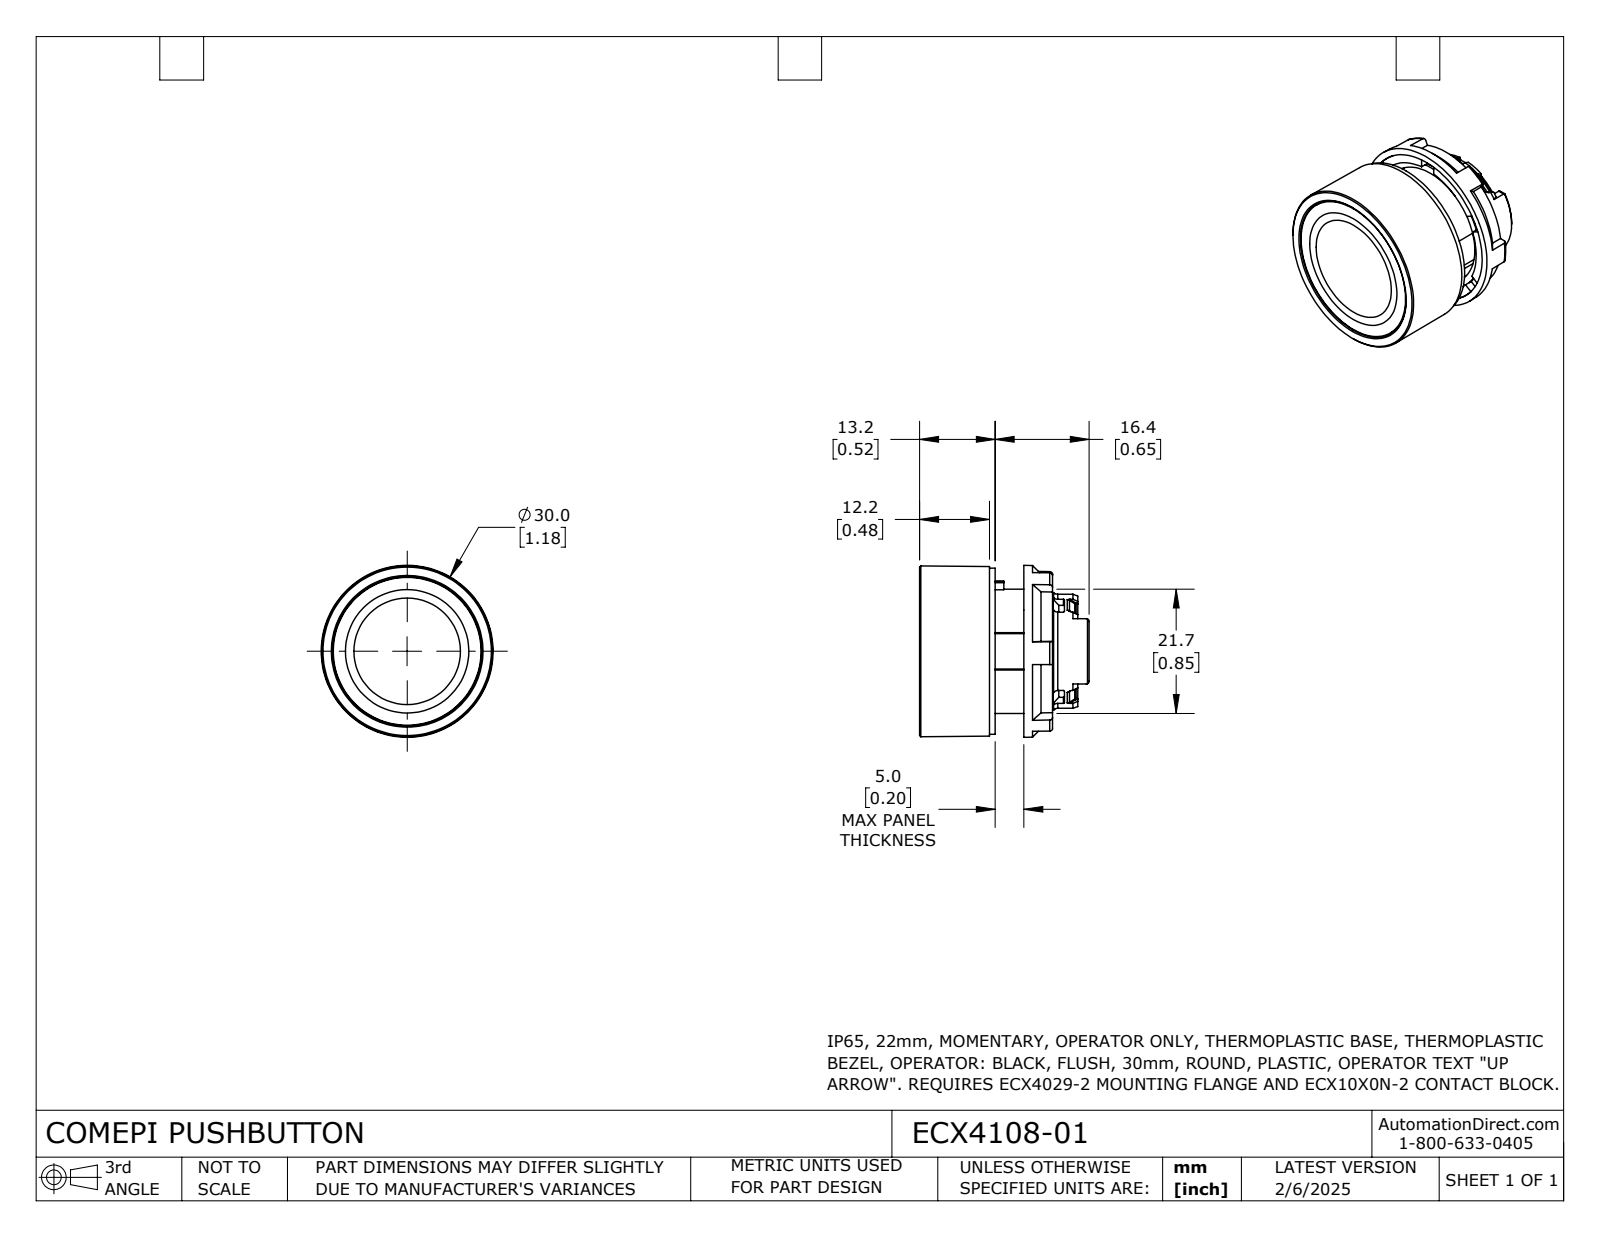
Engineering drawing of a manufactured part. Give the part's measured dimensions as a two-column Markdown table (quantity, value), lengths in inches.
| quantity | value |
| --- | --- |
| part name | ECX4108-01 |
| STEP written by | SolidWorks 2024 (CONFIG_CONTROL_DESIGN) |
| units | inches |
| bodies | 3 solids, 398 faces (134 planar, 111 cylindrical, 153 other) |
| overall size | 1.181 × 1.181 × 1.165 |
| volume | 0.472 in³ |
| surface area | 16.55 in² |
| round holes (diameter × count) | 0.531 × 1, 0.713 × 1, 0.866 × 1 |
| round bosses / shafts (diameter × count) | 1.142 × 1, 1.016 × 1, 0.965 × 1, 0.854 × 1, 0.807 × 1, 0.787 × 1, 0.748 × 1, 0.728 × 1 |
| partial cylindrical surfaces (radius × count) | 0.008 × 24, 0.02 × 8, 0.01 × 2, 0.293 × 1, 0.344 × 1, 0.348 × 1, 0.366 × 1 |
| main face-to-face distances | 0.409, 0.039, 0.433, 0.472, 0.236, 0.394, 0.197, 0.449, 0.512, 0.217 |
